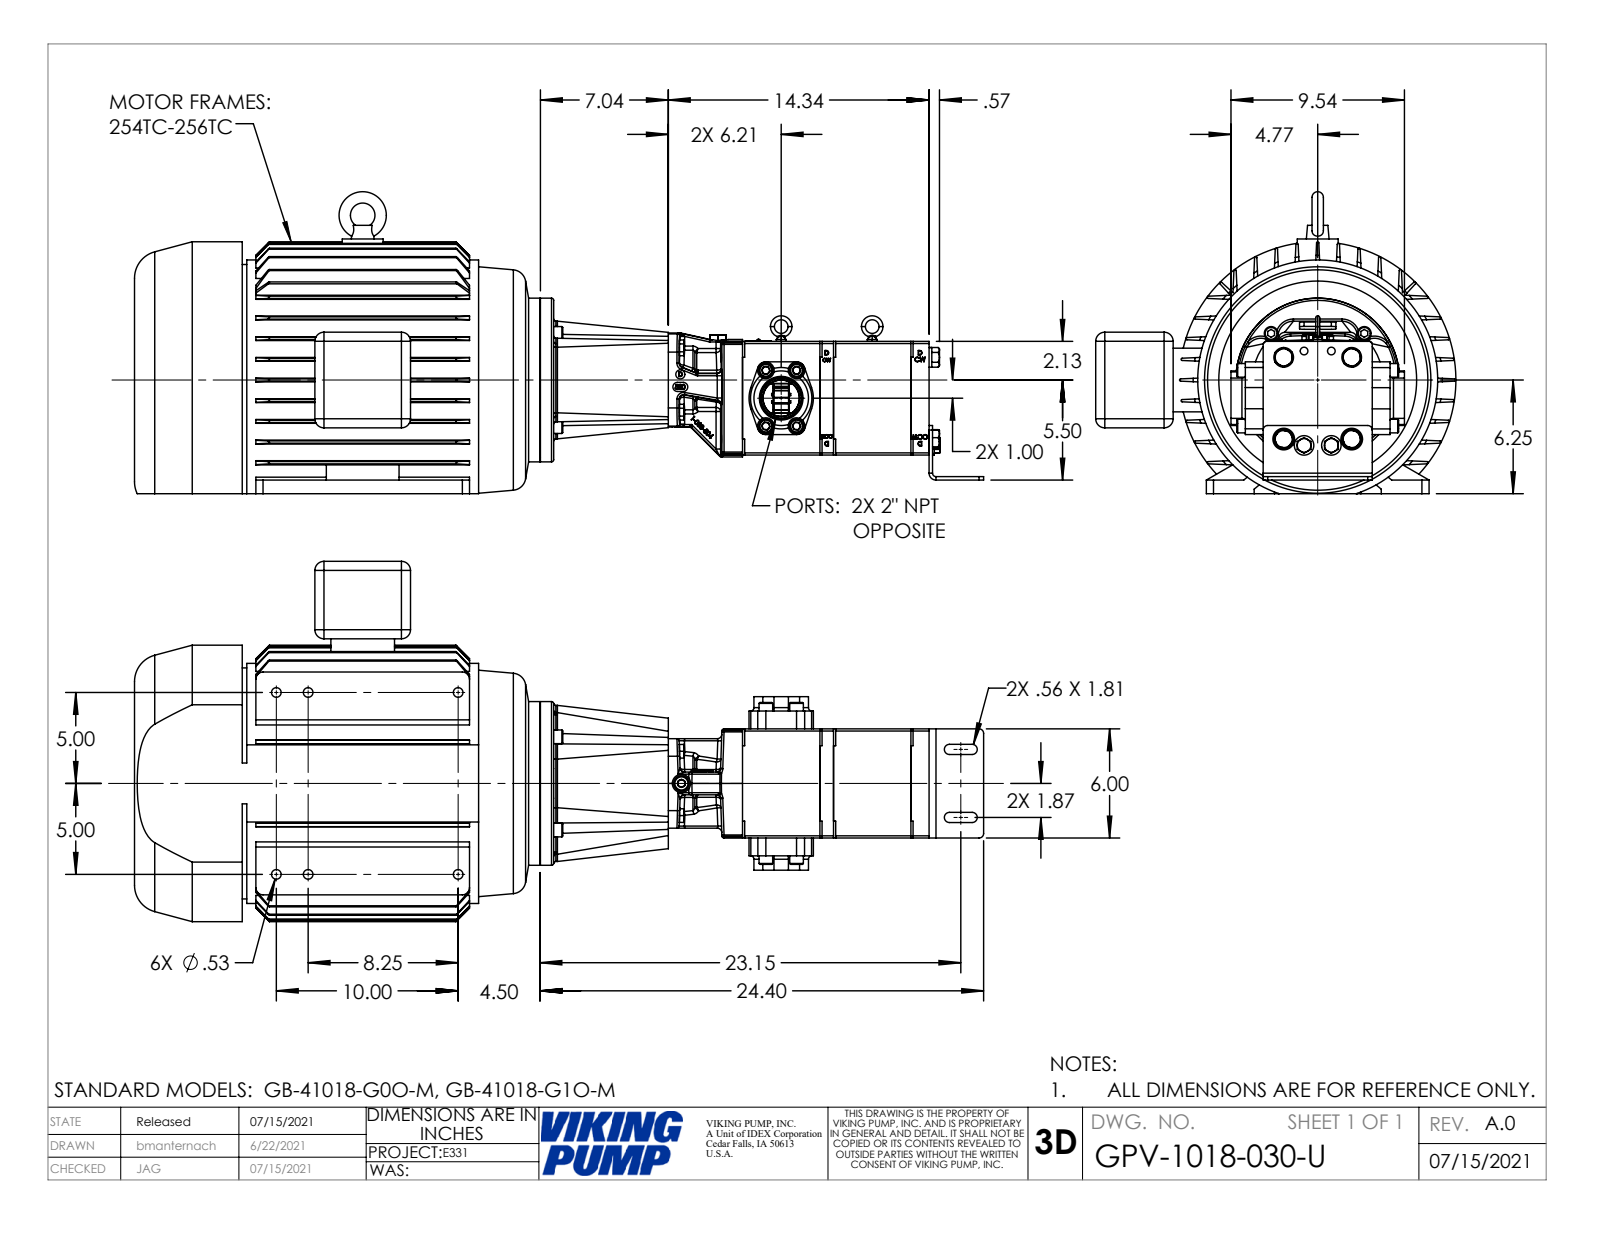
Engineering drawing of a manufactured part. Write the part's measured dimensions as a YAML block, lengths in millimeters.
part_name: "GPV-1018-030-U"
step_written_by: "SolidWorks 2020 (AUTOMOTIVE_DESIGN)"
units: millimeters
bodies: {solids: 1, faces: 3651, planar: 2016, cylindrical: 388, other: 1247}
overall_size: [1186.2, 503.2, 421.7]
volume: 67910000
surface_area: 1847000
round_holes:
  - {diameter: 13.5, count: 6}
  - {diameter: 10.7, count: 4}
  - {diameter: 13.5, count: 4}
  - {diameter: 16, count: 4}
  - {diameter: 23.1, count: 4}
  - {diameter: 30.2, count: 2}
  - {diameter: 12.7, count: 1}
  - {diameter: 25.4, count: 1}
  - {diameter: 30, count: 1}
  - {diameter: 216, count: 1}
round_bosses_or_shafts:
  - {diameter: 19.1, count: 8}
  - {diameter: 27.4, count: 4}
  - {diameter: 15.9, count: 4}
  - {diameter: 27.3, count: 2}
  - {diameter: 386.1, count: 1}
  - {diameter: 335.3, count: 1}
  - {diameter: 322.6, count: 1}
  - {diameter: 228.6, count: 1}
partial_cylinders:
  - {radius: 3, count: 50}
  - {radius: 6.4, count: 32}
  - {radius: 1.6, count: 24}
  - {radius: 12.7, count: 12}
  - {radius: 21.6, count: 8}
  - {radius: 1.6, count: 5}
  - {radius: 1.5, count: 4}
  - {radius: 7.1, count: 4}
face_to_face_distances: [28, 230.7, 202.6, 56.4, 174.3, 28.3, 201.1, 29.6, 173, 144.7]
hole_center_spacings: [254, 29.8, 40.7, 42.9, 44.5, 44.8, 57.1, 67.1]
